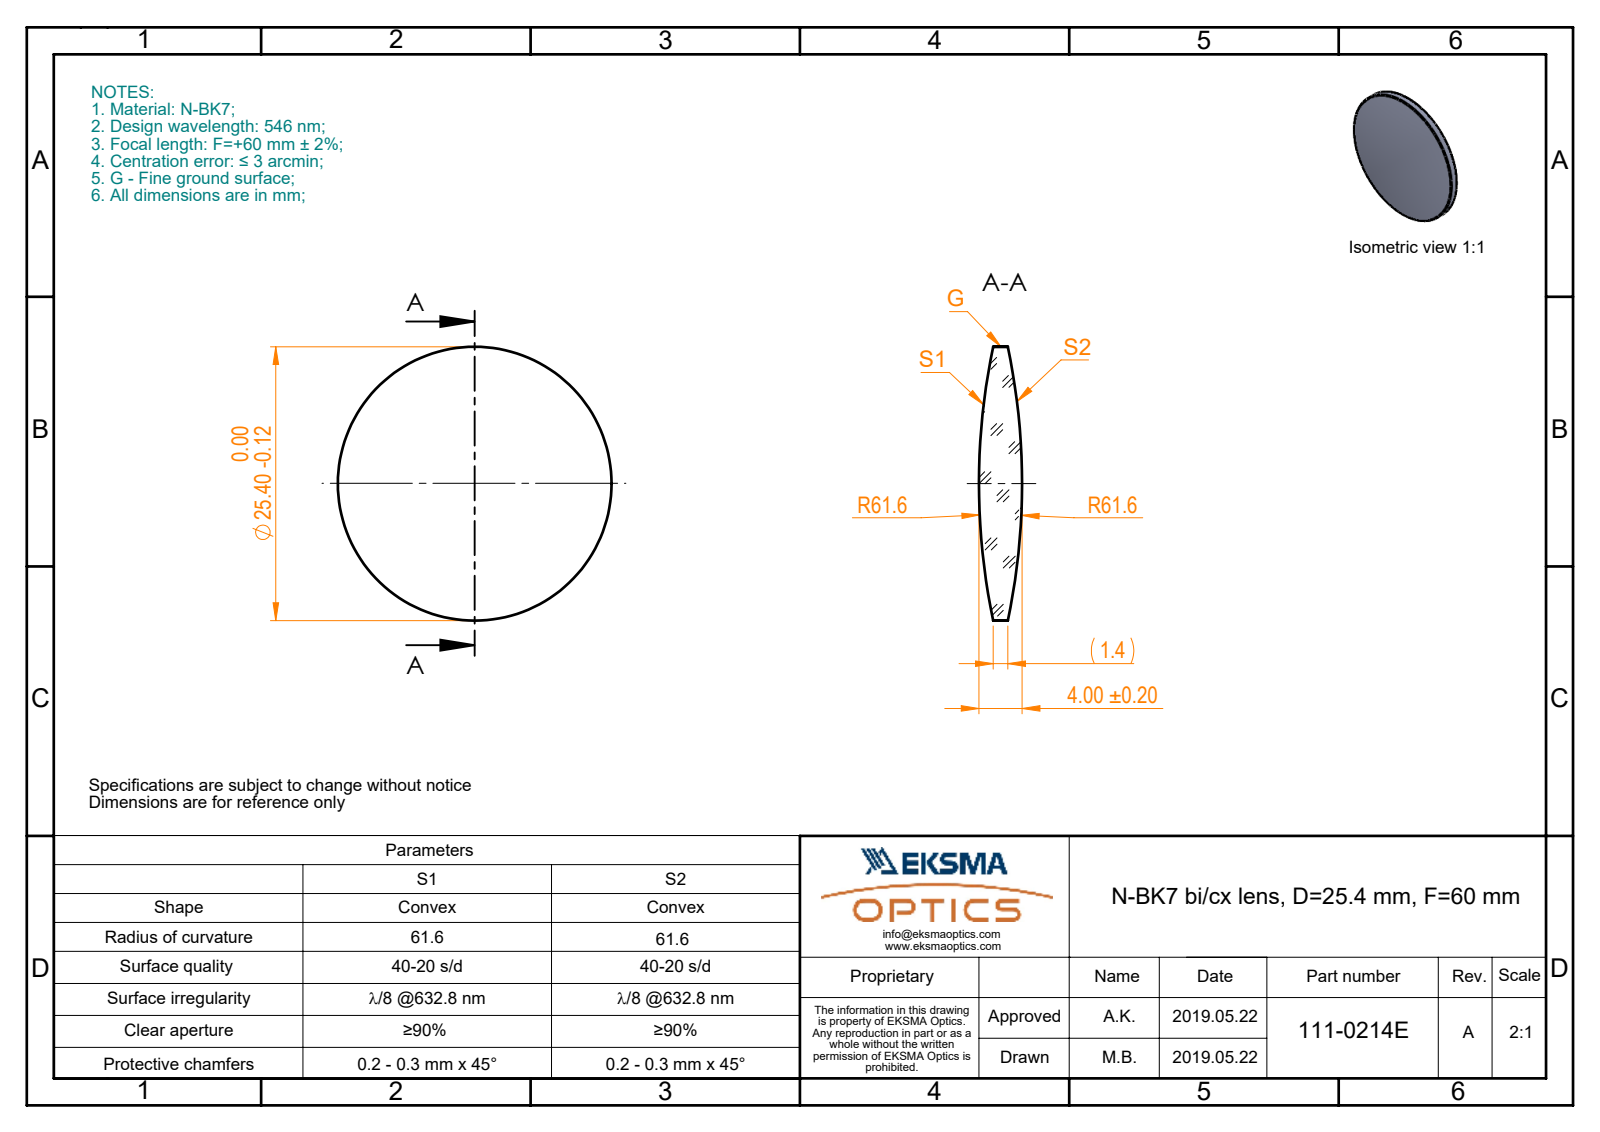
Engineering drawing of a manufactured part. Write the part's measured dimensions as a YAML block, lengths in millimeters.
part_name: "111-0214E BK7 bi-cx 25.4 F60"
step_written_by: "SolidWorks 2017 (CONFIG_CONTROL_DESIGN)"
units: millimeters
bodies: {solids: 1, faces: 6, planar: 0, cylindrical: 2, other: 4}
overall_size: [25.4, 25.4, 4]
volume: 1358
surface_area: 1132
round_bosses_or_shafts:
  - {diameter: 25.4, count: 1}
